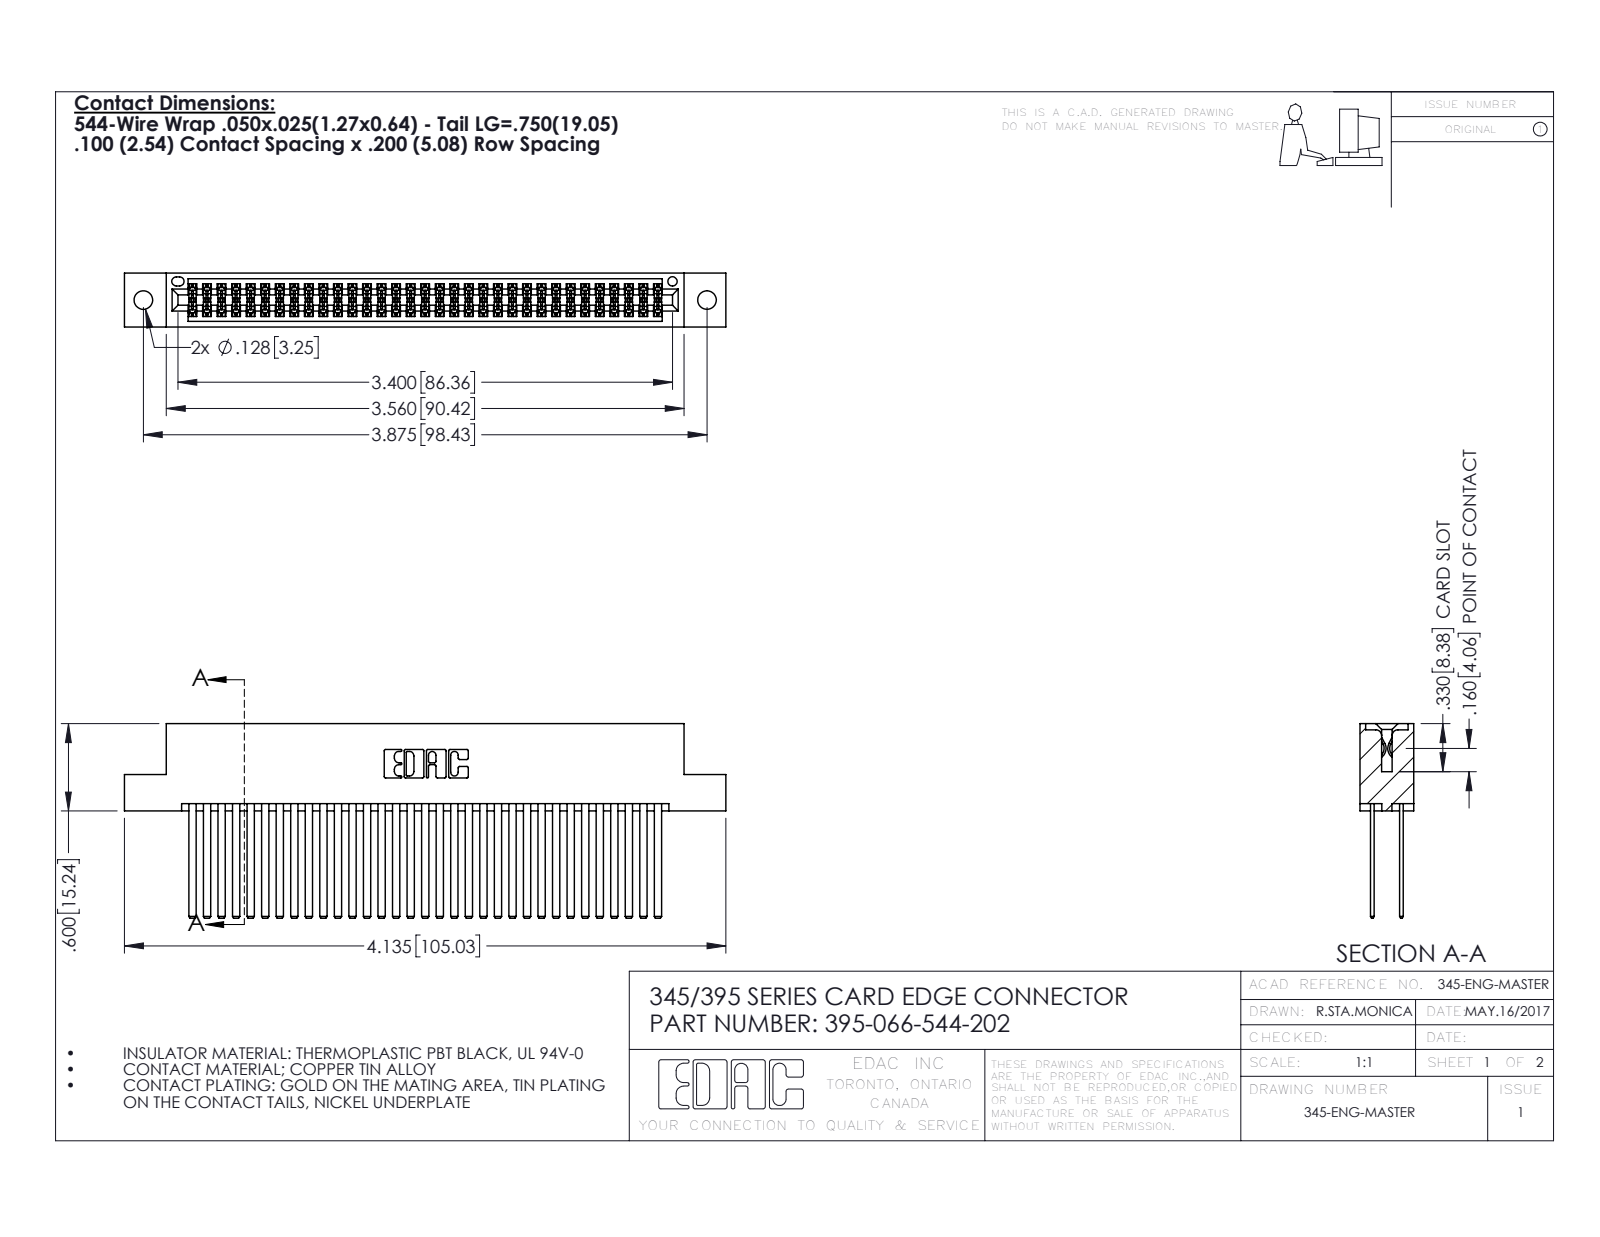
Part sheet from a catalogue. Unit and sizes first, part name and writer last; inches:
Units: inches
Overall size (bounding box): 4.135 × 1.337 × 0.37
Round holes (diameter × count): ⌀0.128 ×2, ⌀0.064 ×1
Partial cylindrical surfaces — rounded edges, fillets, slot ends (radius × count): R0.006 ×99, R0.01 ×22, R0.007 ×6, R0.031 ×6, R0.026 ×3, R0.014 ×2, R0.019 ×2, R0.022 ×2
Main face-to-face distances: 0.2, 0.025, 0.298, 0.072, 0.098, 0.272, 0.225, 0.175, 0.37, 0.05
Hole centre spacings: 0.27, 3.64, 3.875
Volume: 0.672 in³ · Surface area: 28.73 in²
Bodies: 67 solids, 3030 faces (1994 planar, 1036 cylindrical, 0 other)
Part name (STEP PRODUCT): 395-066-544-202; 345-292-001_345-293-144; 345 Part_Flush Mounting Lugs - 0.128 Dia
STEP written by: SolidWorks 2016 (CONFIG_CONTROL_DESIGN)
